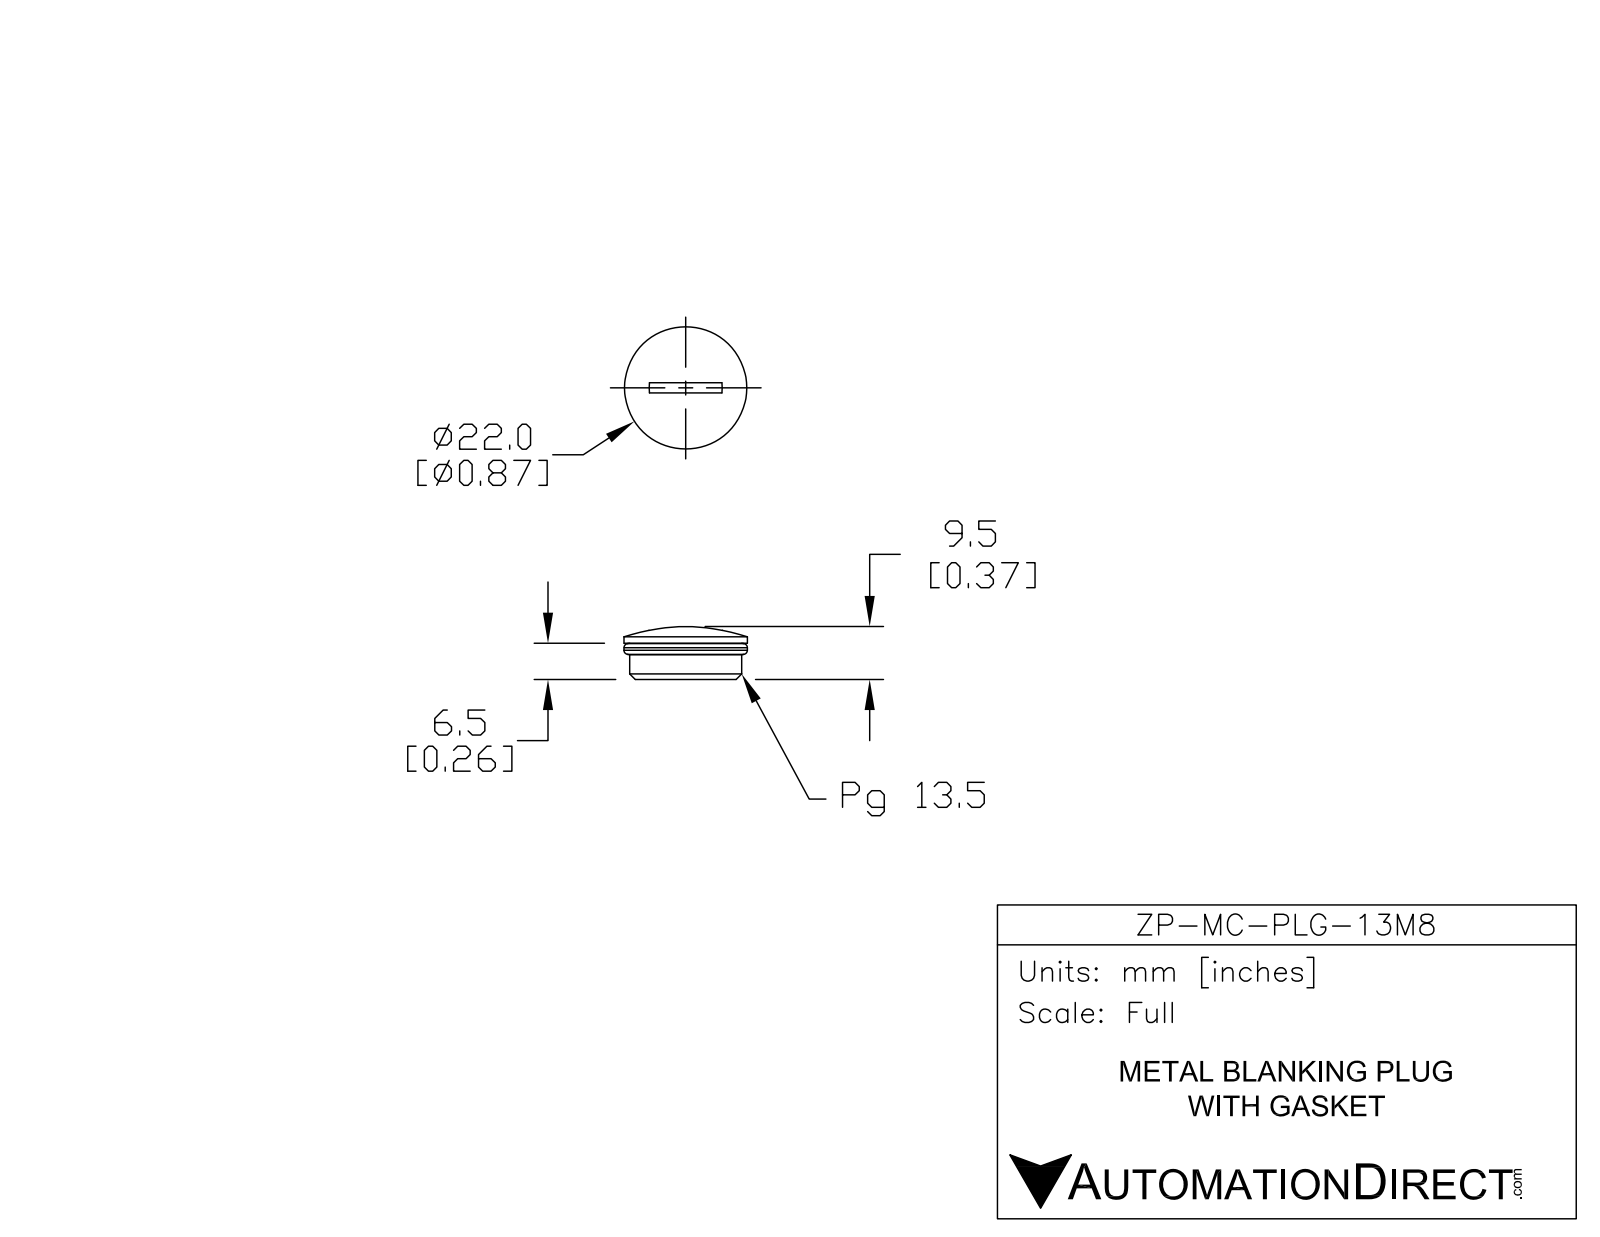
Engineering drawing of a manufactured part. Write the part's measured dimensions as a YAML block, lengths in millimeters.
part_name: "ZP-MC-PLG-13M8"
step_written_by: "SolidWorks 2014 (AUTOMOTIVE_DESIGN)"
units: millimeters
bodies: {solids: 1, faces: 26, planar: 5, cylindrical: 9, other: 12}
overall_size: [22.2, 22.2, 9.52]
volume: 1347
surface_area: 1736
round_holes:
  - {diameter: 16.9, count: 1}
round_bosses_or_shafts:
  - {diameter: 22.2, count: 1}
  - {diameter: 20.15, count: 1}
partial_cylinders:
  - {radius: 49.02, count: 1}
face_to_face_distances: [0.73, 6.42, 7.15, 1.86]
